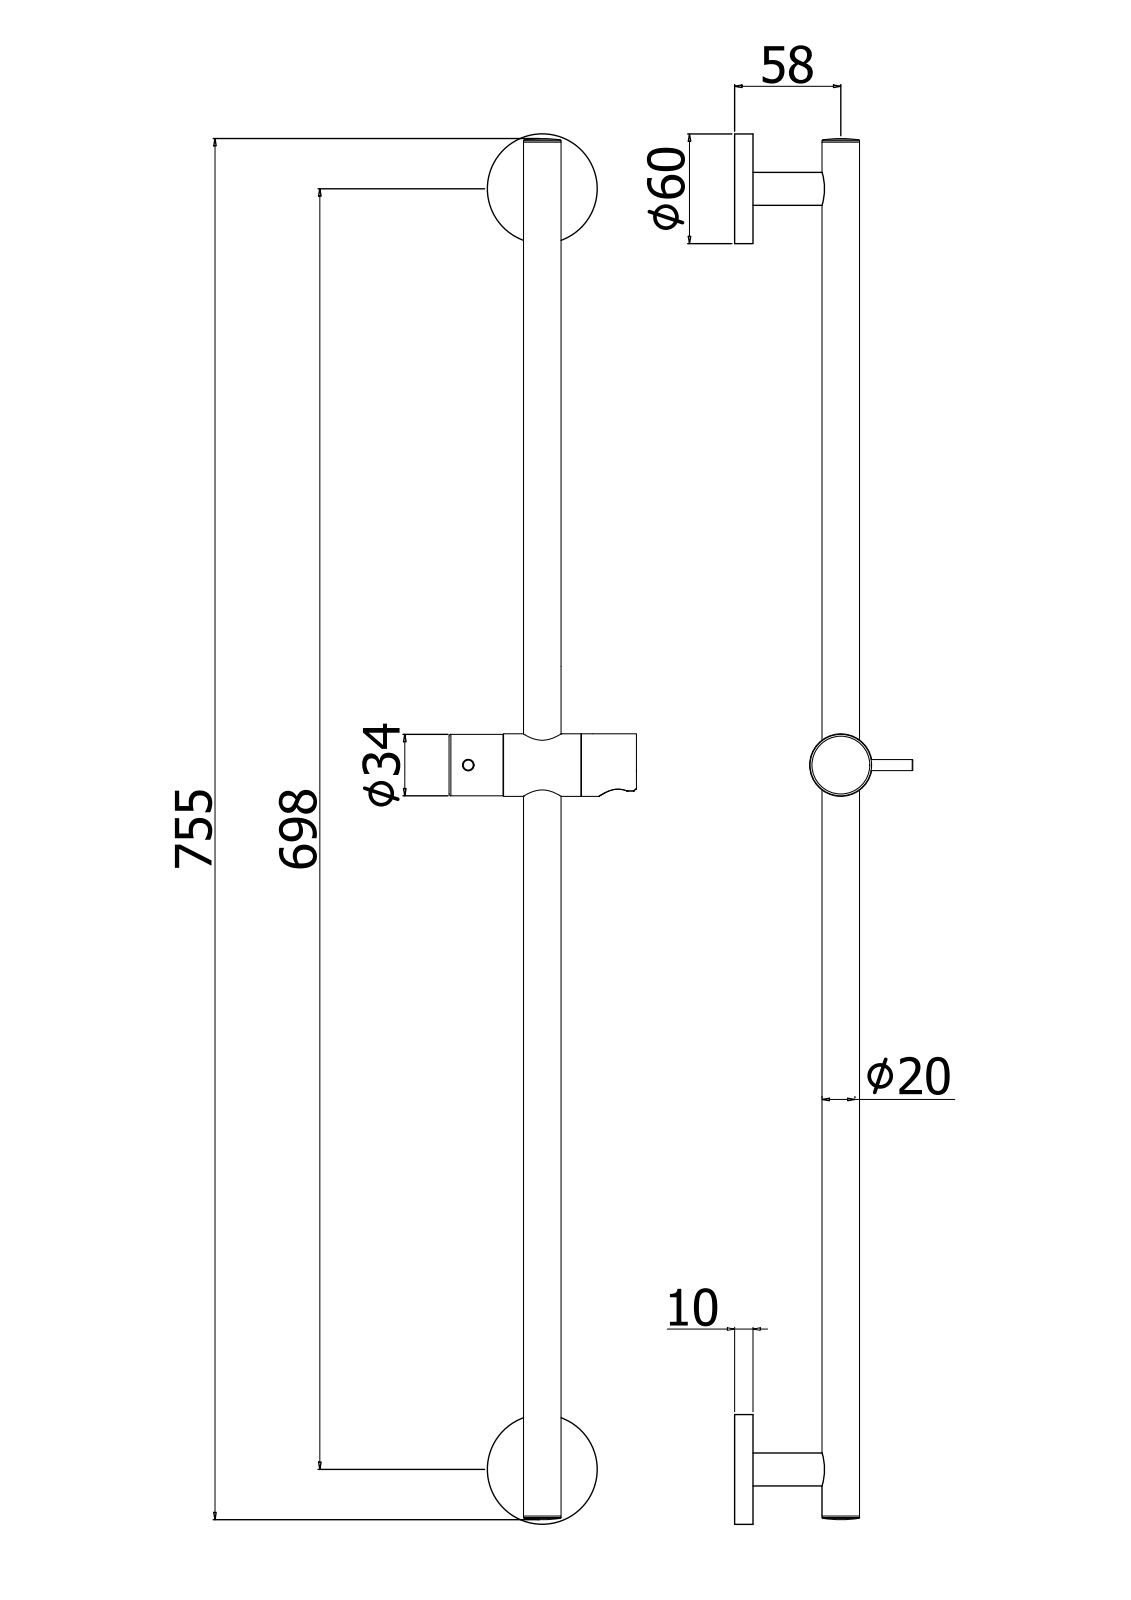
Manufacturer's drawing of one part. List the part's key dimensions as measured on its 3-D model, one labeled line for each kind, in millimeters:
Part name (STEP PRODUCT): ZSAL116CR
STEP written by: CREO PARAMETRIC BY PTC INC, 2020044 (CONFIG_CONTROL_DESIGN)
Units: millimetres
Bodies: 3 solids, 344 faces (137 planar, 72 cylindrical, 135 other)
Overall size (bounding box): 760 × 93 × 77
Volume: 349 796 mm³ · Surface area: 92 429 mm²
Round holes (diameter × count): ⌀51 ×2, ⌀4 ×1, ⌀12 ×1
Round bosses / shafts (diameter × count): ⌀9 ×3, ⌀60 ×2, ⌀18 ×2, ⌀34 ×1, ⌀28 ×1, ⌀20 ×1, ⌀14 ×1, ⌀11.4 ×1
Partial cylindrical surfaces — rounded edges, fillets, slot ends (radius × count): R0.3 ×4, R1.9 ×4, R2 ×4, R1.91 ×2, R1.93 ×2, R4.5 ×2, R86.71 ×2
Main face-to-face distances: 2, 8, 10, 1, 9, 7, 0.5, 40.7, 2.4, 93
Hole centre spacings: 700
